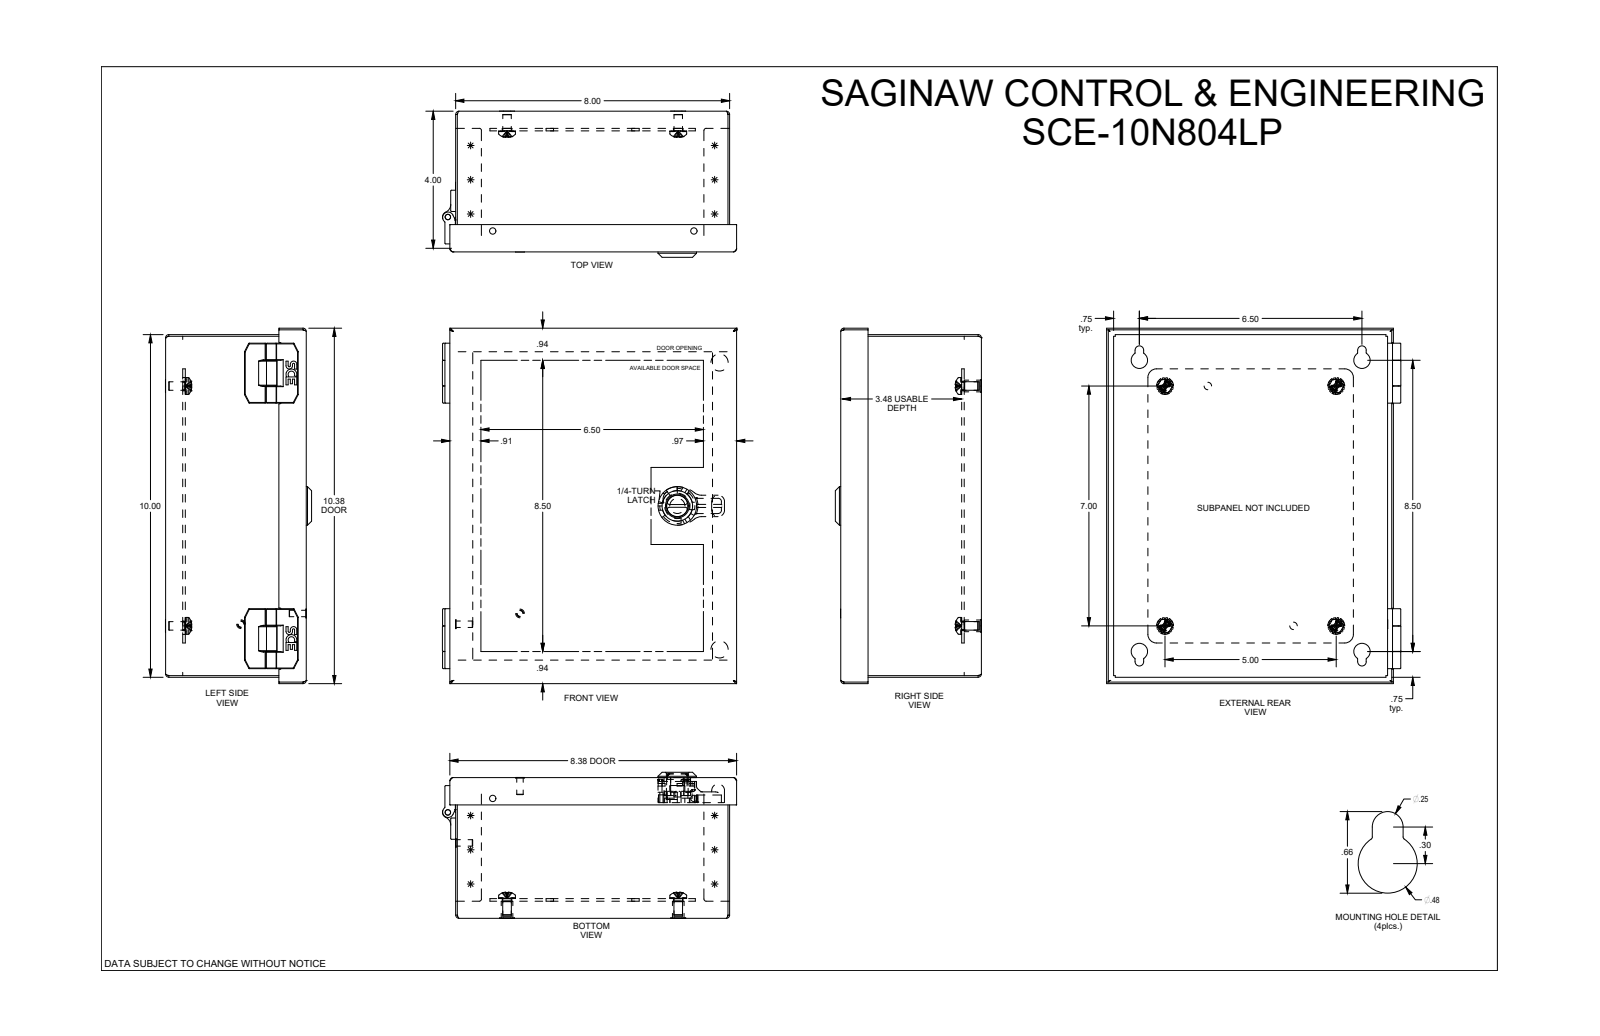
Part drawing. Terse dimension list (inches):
name: SCE-10N804LP
written by: SolidWorks 2019 (AUTOMOTIVE_DESIGN)
unit: in
bodies: 31 solids, 2413 faces (710 planar, 851 cylindrical, 852 other)
size: 10.375 × 8.593 × 4.267
volume: 26.46 in³; area: 843.5 in²
holes: 4× ⌀0.17, 4× ⌀0.25, 4× ⌀0.281, 4× ⌀0.329, 4× ⌀0.343, 4× ⌀0.48, 3× ⌀0.193, 2× ⌀0.218, 1× ⌀0.158, 1× ⌀0.187, 1× ⌀0.44, 1× ⌀0.635
bosses: 4× ⌀0.492, 4× ⌀0.479, 4× ⌀0.341, 4× ⌀0.248, 4× ⌀0.237, 4× ⌀0.16, 2× ⌀0.5, 2× ⌀0.323
rounds: 253× R0.01, 132× R0.106, 95× R0.02, 76× R0.005, 25× R0.06, 24× R0.015, 24× R0.025, 6× R0.055
face distances: 0.06, 4.047, 3.987, 4.107, 7.94, 9.94, 0.5, 0.44, 0.575, 0.515
hole spacings: 1.061, 5.799, 7.75, 7.786, 9.65, 7.75, 7.826, 0.555
